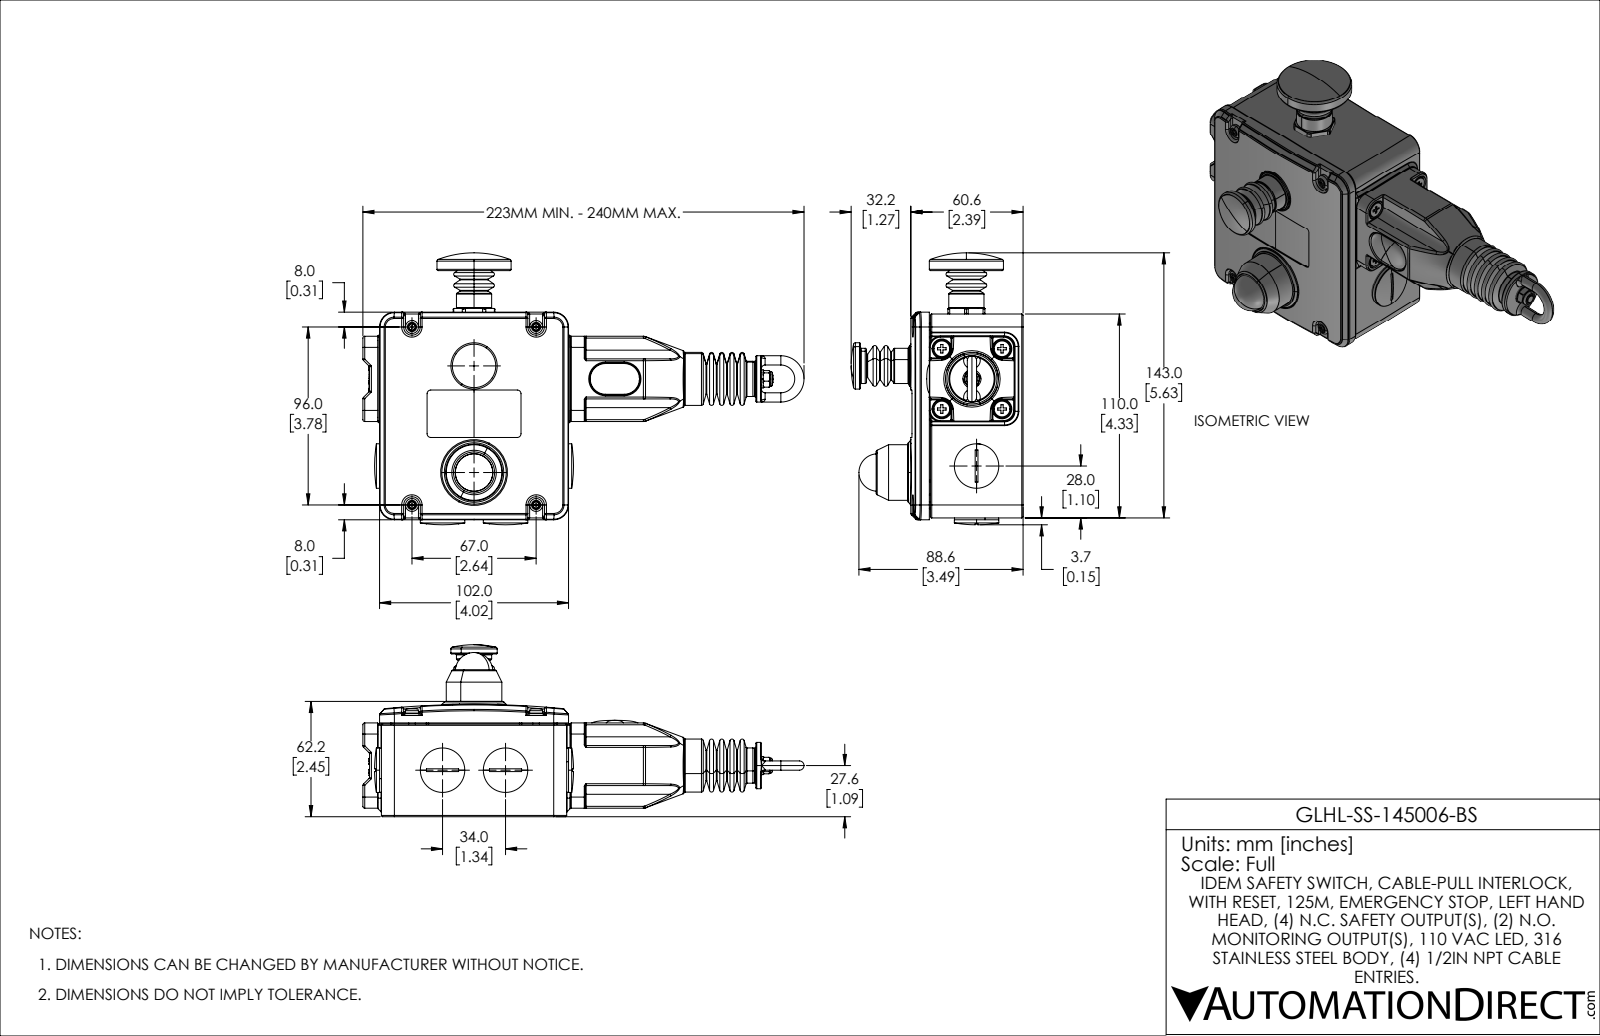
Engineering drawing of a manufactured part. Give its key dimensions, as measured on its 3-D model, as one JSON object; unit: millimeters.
{"part_name": "GLHL-SS-145006-BS", "step_written_by": "SolidWorks 2021 (AUTOMOTIVE_DESIGN)", "units": "millimeters", "bodies": {"solids": 47, "faces": 4430, "planar": 1376, "cylindrical": 1433, "other": 1621}, "overall_size": [238.1, 146.7, 92.8], "volume_mm3": 312000, "surface_area_mm2": 193400, "round_holes": [[5, 9], [5.3, 9], [9.6, 8], [4.1, 7], [9, 6], [3.3, 4], [4, 4], [4.8, 4], [5.4, 4], [5.8, 4], [1.7, 3], [2.6, 3]], "round_bosses_or_shafts": [[5, 11], [8.5, 8], [4.4, 8], [7, 5], [20, 4], [3.5, 4], [1.3, 4], [24, 3]], "partial_cylinders_radius": [[0.5, 221], [1, 163], [0.2, 76], [0.7, 48], [0.3, 18], [0.2, 14], [2, 14], [0.1, 10]], "face_to_face_distances": [1, 2, 3.5, 55.4, 52.5, 2.9, 102, 4, 110, 8.5], "hole_center_spacings": [32.5, 32.5, 23, 9.5, 5.8, 22.9, 23, 23]}
